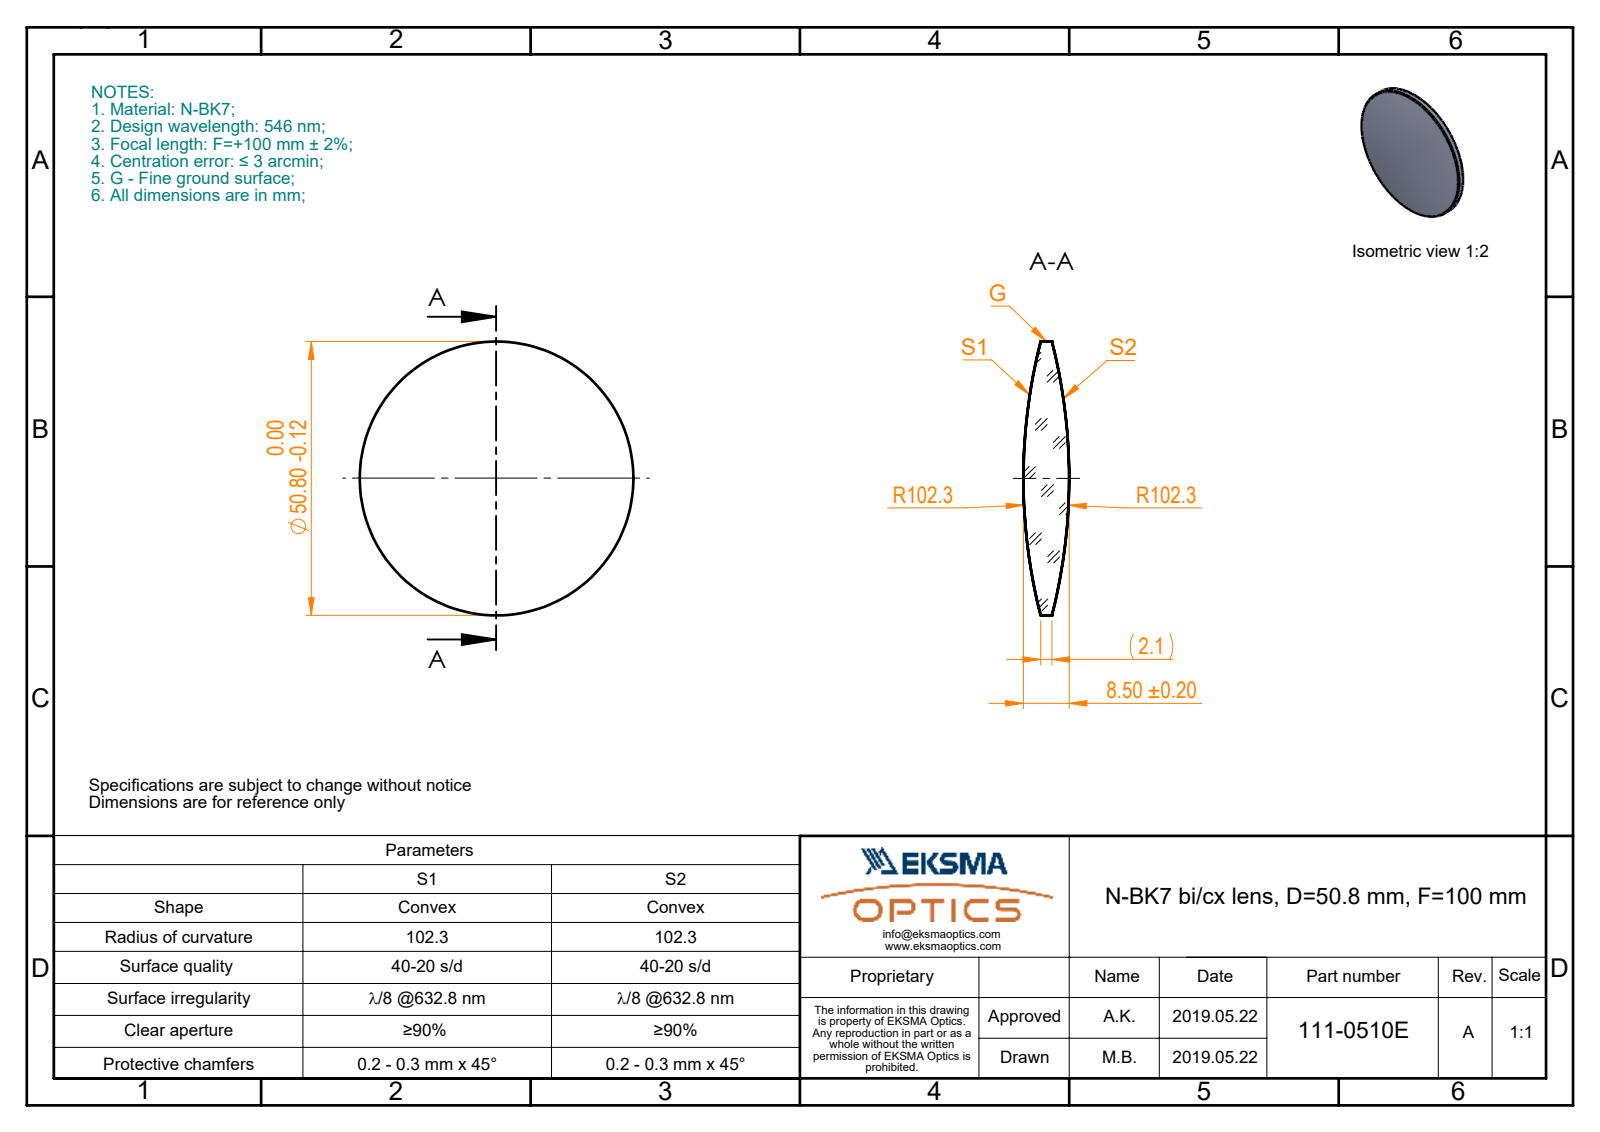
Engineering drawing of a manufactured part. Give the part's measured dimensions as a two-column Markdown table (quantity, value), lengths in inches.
| quantity | value |
| --- | --- |
| part name | 111-0510E BK7 bi-cx 50.8 F100 |
| STEP written by | SolidWorks 2017 (CONFIG_CONTROL_DESIGN) |
| units | inches |
| bodies | 1 solid, 6 faces (0 planar, 2 cylindrical, 4 other) |
| overall size | 2 × 2 × 0.335 |
| volume | 0.657 in³ |
| surface area | 6.901 in² |
| round bosses / shafts (diameter × count) | 2 × 1 |
